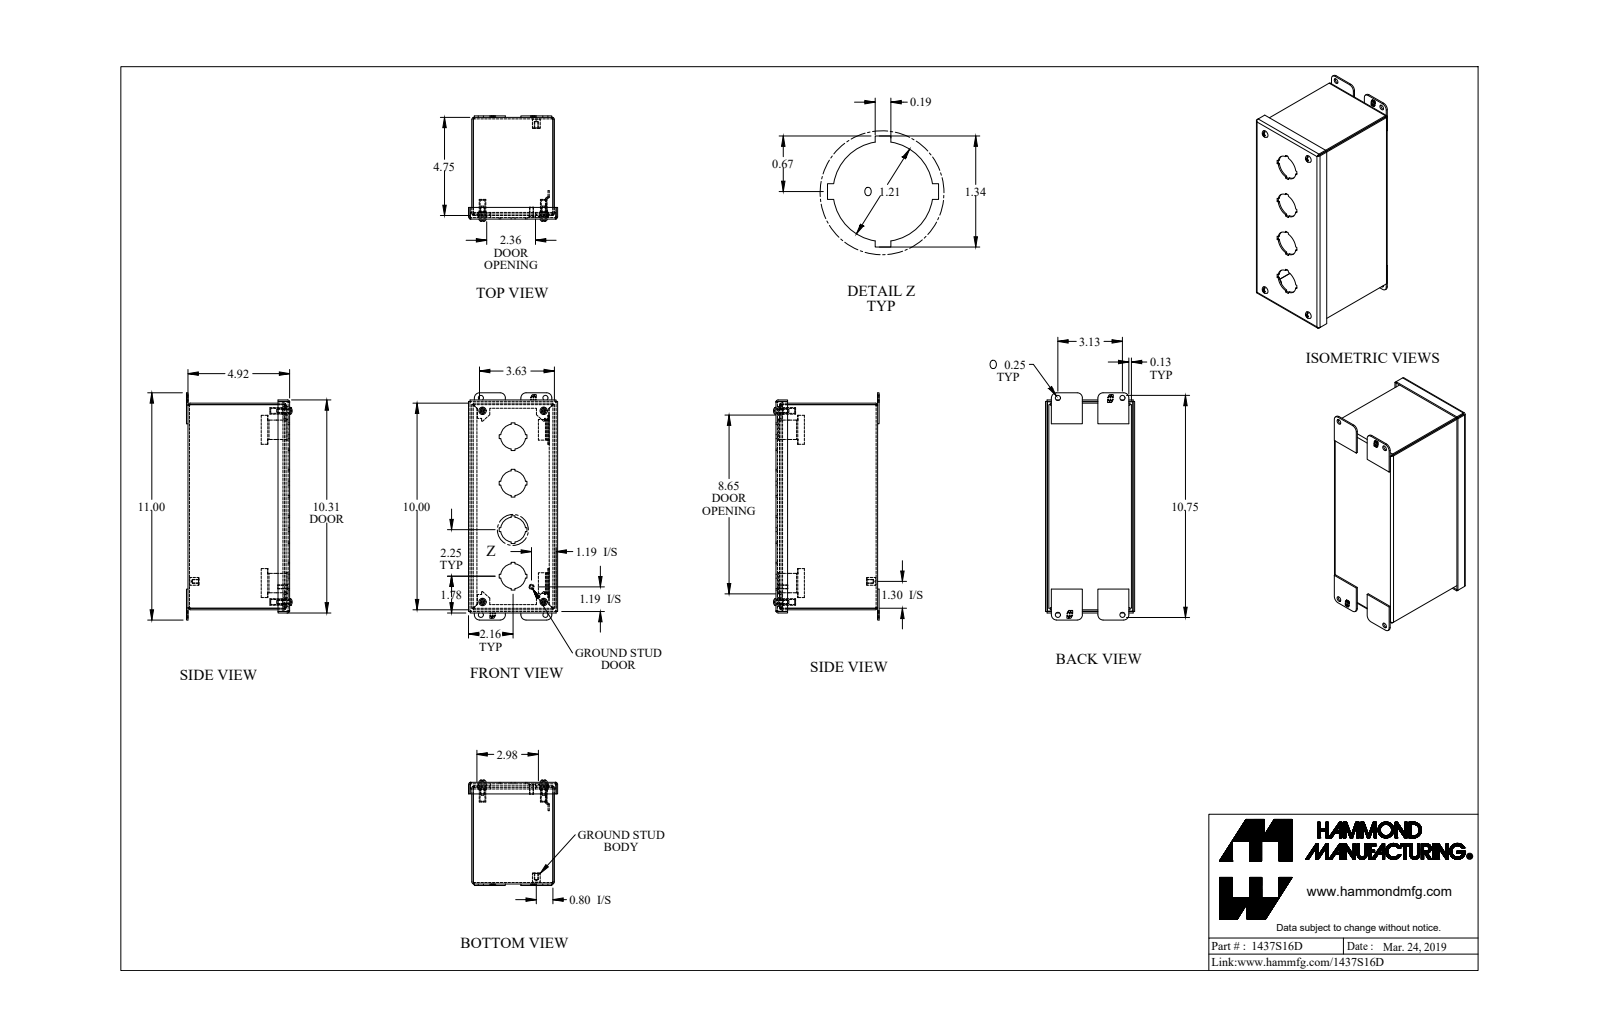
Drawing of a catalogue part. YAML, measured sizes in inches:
part_name: "1437S16D_Default"
step_written_by: "SolidWorks 2019 (CONFIG_CONTROL_DESIGN)"
units: inches
bodies: {solids: 23, faces: 669, planar: 471, cylindrical: 168, other: 30}
overall_size: [11, 5.104, 4.312]
volume: 19.97
surface_area: 533.6
round_holes:
  - {diameter: 0.25, count: 8}
  - {diameter: 0.065, count: 4}
  - {diameter: 0.239, count: 4}
  - {diameter: 0.253, count: 4}
  - {diameter: 0.406, count: 4}
  - {diameter: 1.21, count: 4}
  - {diameter: 0.156, count: 1}
round_bosses_or_shafts:
  - {diameter: 0.19, count: 5}
  - {diameter: 0.406, count: 4}
  - {diameter: 0.315, count: 4}
  - {diameter: 0.148, count: 4}
  - {diameter: 0.375, count: 1}
  - {diameter: 0.25, count: 1}
partial_cylinders:
  - {radius: 0.036, count: 12}
  - {radius: 0.108, count: 12}
  - {radius: 0.25, count: 8}
  - {radius: 0.029, count: 4}
  - {radius: 0.086, count: 4}
  - {radius: 0.171, count: 4}
  - {radius: 0.125, count: 2}
face_to_face_distances: [0.072, 3.928, 4.85, 4.922, 4, 3.856, 4.778, 9.928, 0.156, 4.084]
hole_center_spacings: [9.25, 9.875, 10.333, 2.961, 3.107, 9.712, 2.962, 0.63]
